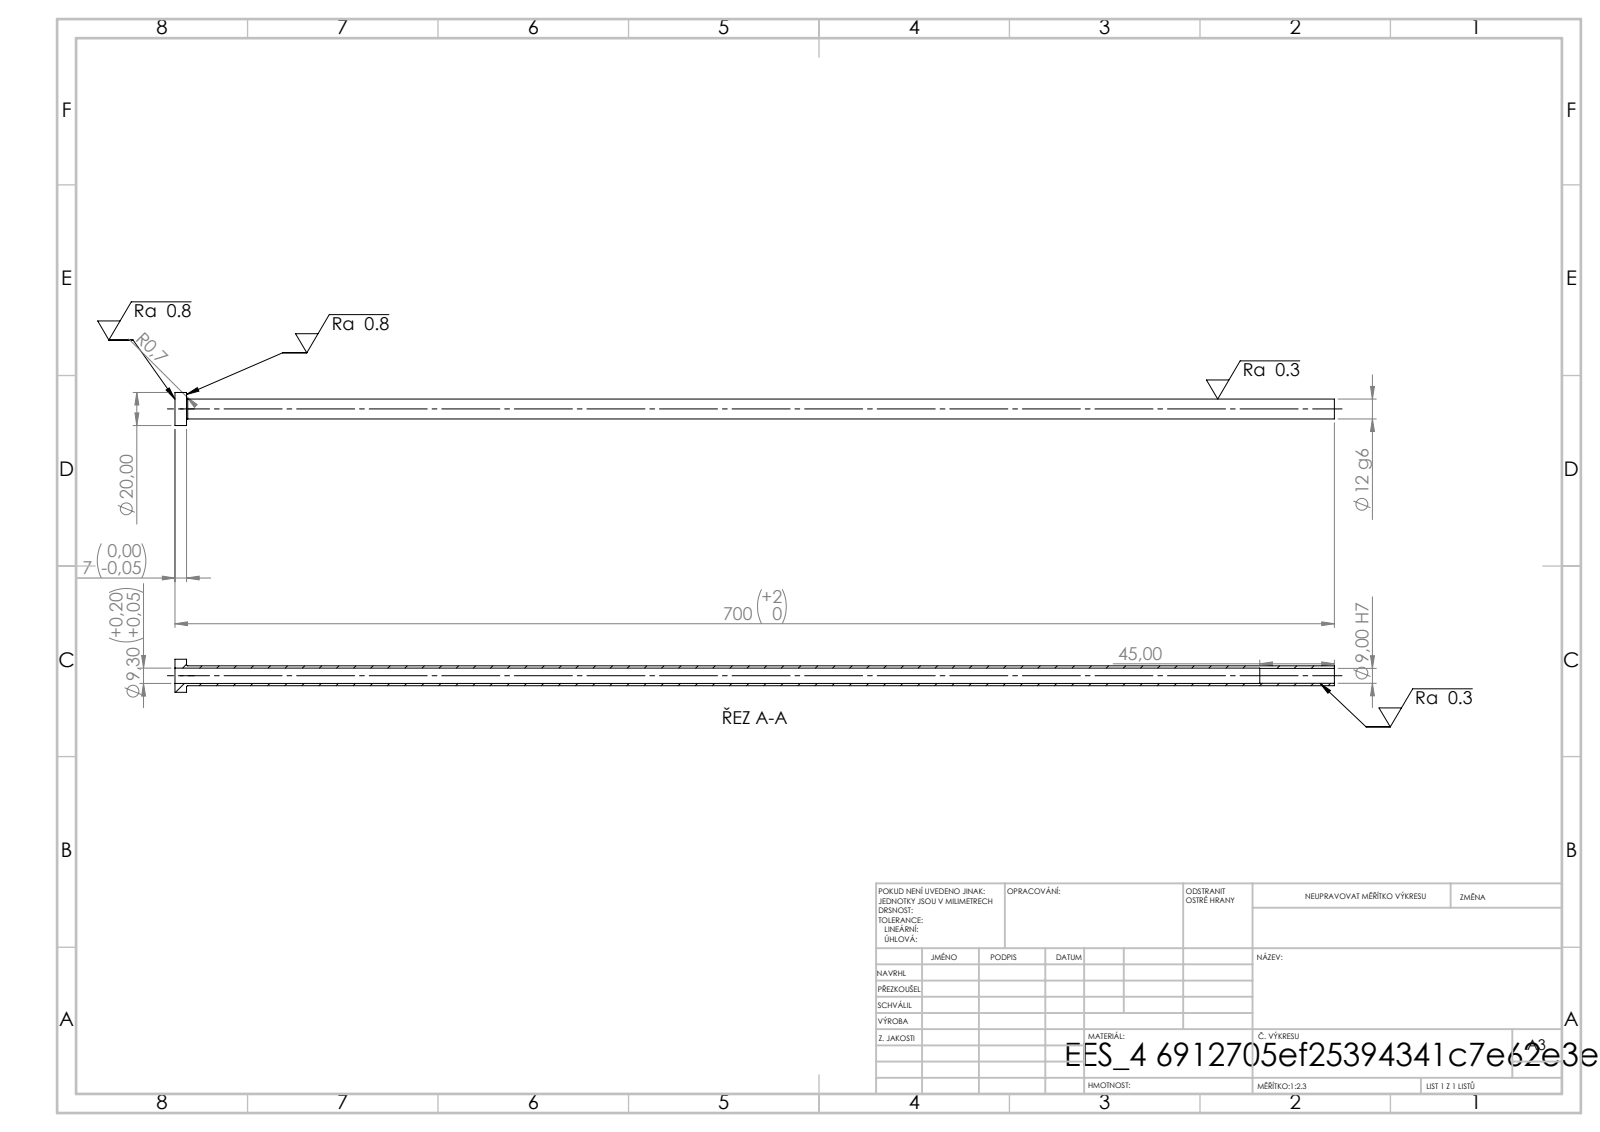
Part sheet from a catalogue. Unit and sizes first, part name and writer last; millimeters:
Units: millimetres
Overall size (bounding box): 700 × 20 × 20
Round holes (diameter × count): ⌀9 ×1, ⌀9.3 ×1
Round bosses / shafts (diameter × count): ⌀20 ×1, ⌀12 ×1
Main face-to-face distances: 7, 700, 693, 655, 648, 45
Volume: 33 223 mm³ · Surface area: 47 465 mm²
Bodies: 1 solid, 14 faces (4 planar, 8 cylindrical, 2 other)
STEP written by: SolidWorks 2019 (CONFIG_CONTROL_DESIGN)
